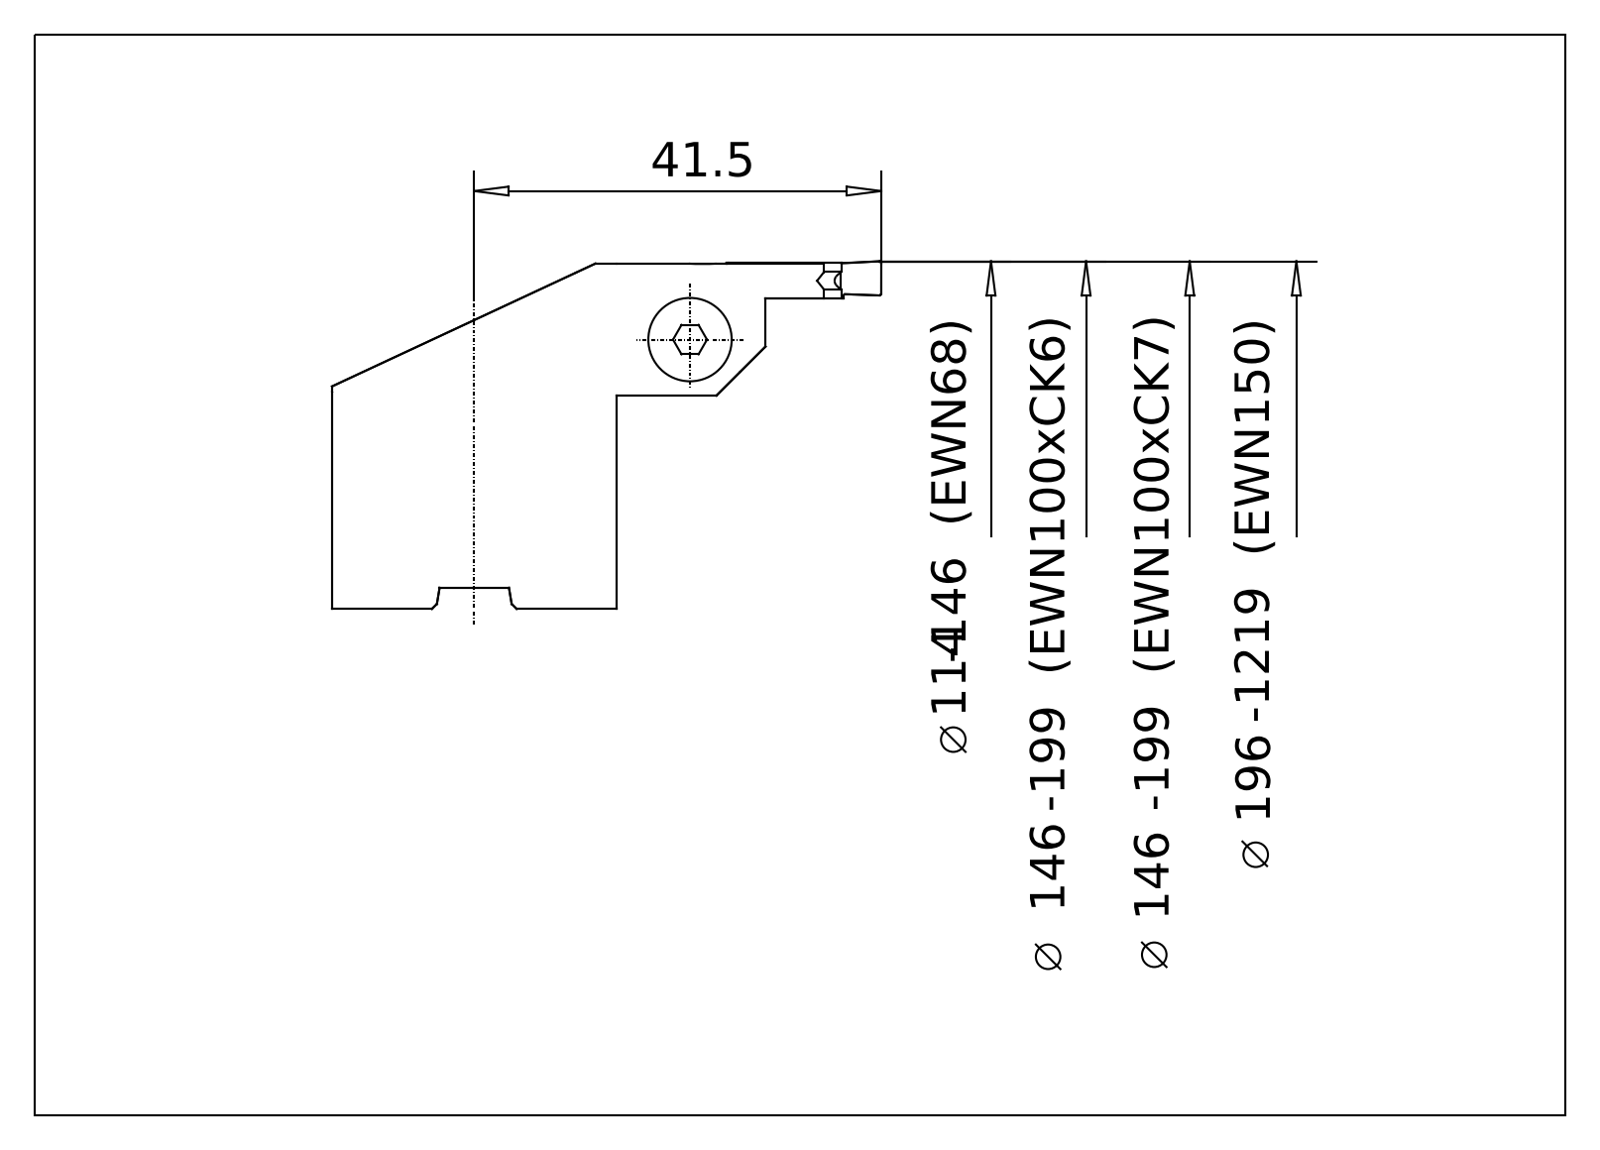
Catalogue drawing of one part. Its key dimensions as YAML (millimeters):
part_name: "626.947 Kaiser ENH 63 S4 114-146 R|626.947 Kaiser ENH 63 S4 114-146 R;Schnitt-Rotation8; 626.947 Kaiser ENH 63 S4 114-146 R|958.425 Kaiser NP 4250 P20C_Einstechplatte 4mm;NONE; 626.947 Kaiser ENH 63 S4 114-146 R|690.183 Kaiser ETL M5x12A;Verrundung1"
step_written_by: "ACIS (automotive_design)"
units: millimeters
bodies: {solids: 3, faces: 136, planar: 79, cylindrical: 39, other: 18}
overall_size: [56, 35.43, 29]
volume: 19612
surface_area: 7781
round_holes:
  - {diameter: 4.2, count: 1}
  - {diameter: 5.3, count: 1}
  - {diameter: 8.05, count: 1}
  - {diameter: 9, count: 1}
  - {diameter: 14, count: 1}
round_bosses_or_shafts:
  - {diameter: 29, count: 1}
  - {diameter: 8.5, count: 1}
  - {diameter: 5, count: 1}
partial_cylinders:
  - {radius: 0.2, count: 4}
  - {radius: 0.1, count: 2}
  - {radius: 1.4, count: 2}
  - {radius: 1.63, count: 2}
  - {radius: 1.26, count: 1}
  - {radius: 5, count: 1}
  - {radius: 56.7, count: 1}
face_to_face_distances: [21.75, 19.6, 2.15, 15, 1.6, 13.4, 7.8, 15.65, 3.95, 6.1]
hole_center_spacings: [11.25]
